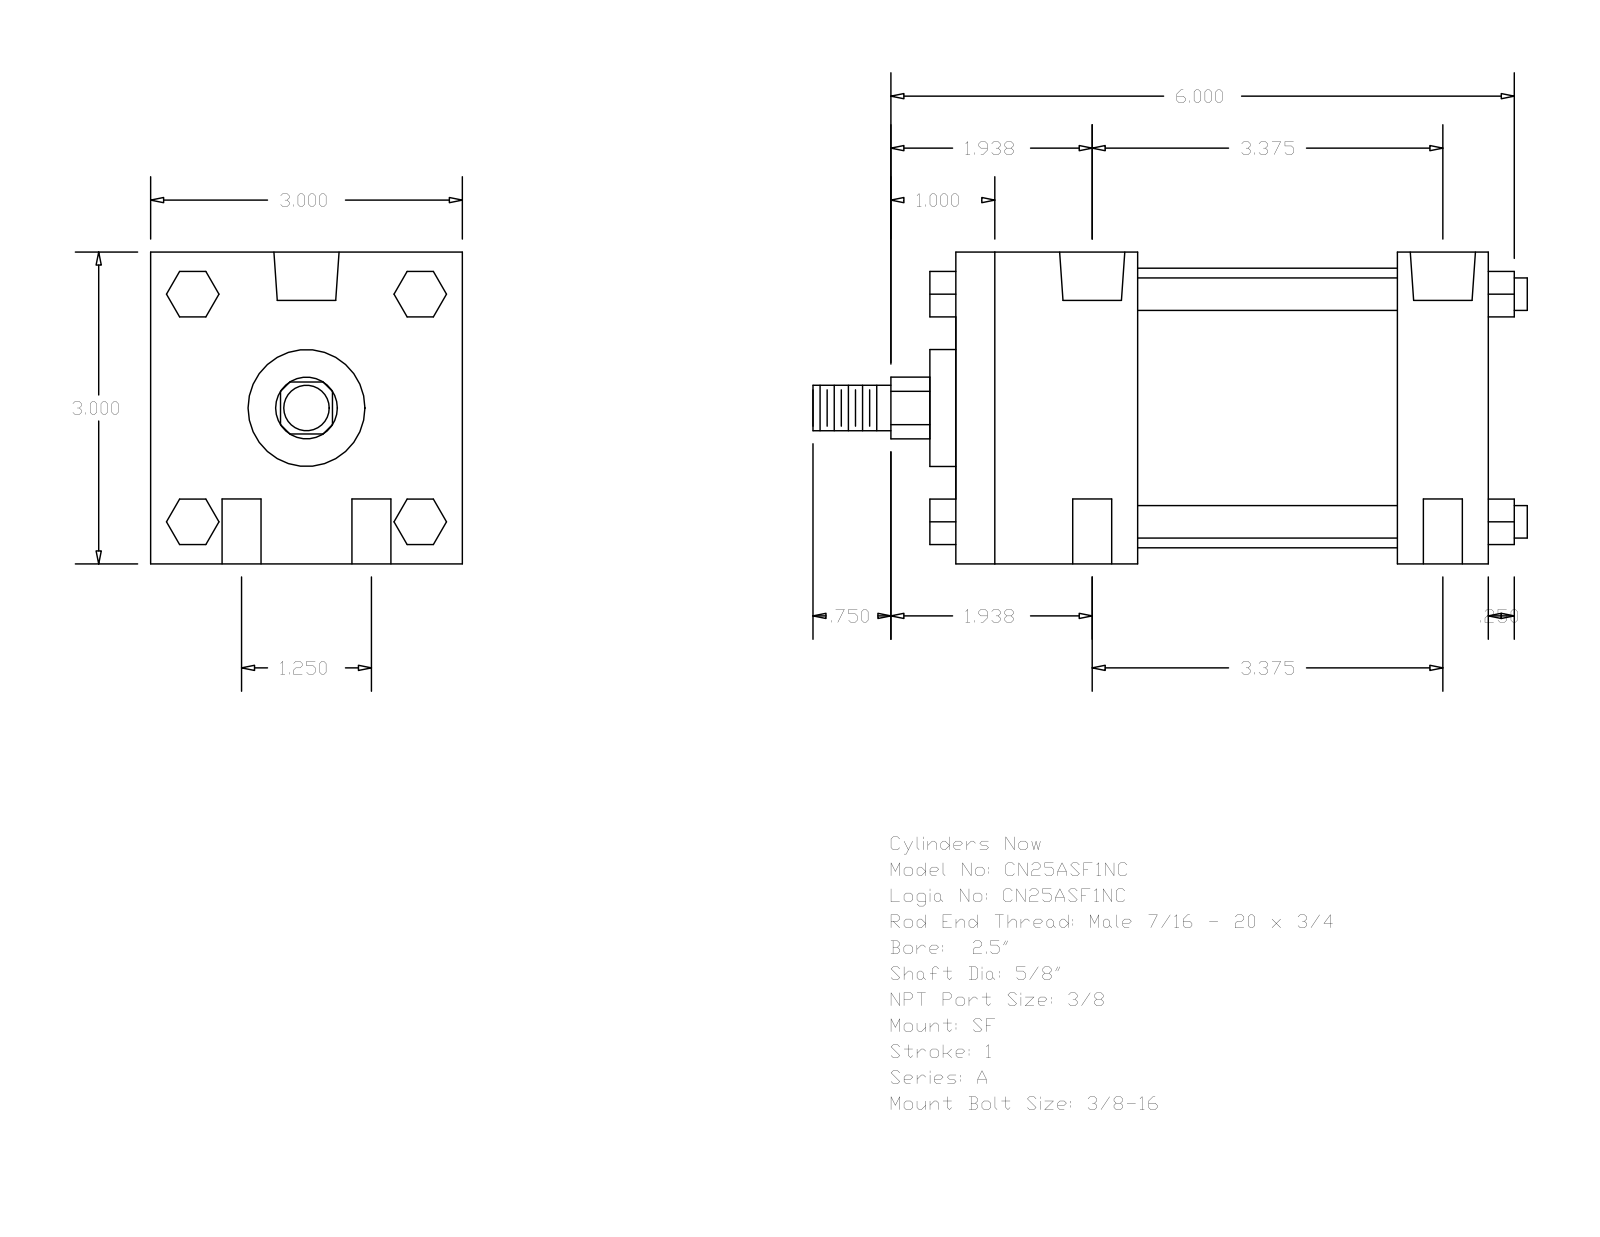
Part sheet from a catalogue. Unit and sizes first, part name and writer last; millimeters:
Units: millimetres
Overall size (bounding box): 174.62 × 76.2 × 76.2
Round holes (diameter × count): ⌀9.53 ×4, ⌀5.56 ×2, ⌀15.93 ×2
Round bosses / shafts (diameter × count): ⌀7.94 ×4, ⌀68.33 ×1, ⌀28.57 ×1, ⌀15.88 ×1, ⌀11.11 ×1
Partial cylindrical surfaces — rounded edges, fillets, slot ends (radius × count): R7.54 ×1
Main face-to-face distances: 76.2, 130.17, 63.5, 44.45, 107.95, 22.22, 85.72, 6.35, 136.52, 50.8
Hole centre spacings: 15.88, 87.19, 85.73, 31.76, 91.42, 90.49
Bodies: 0 solids, 124 faces (94 planar, 30 cylindrical, 0 other)
Part name (STEP PRODUCT): A_SF__0250_0.625
STEP written by: GSSL Pune (CONFIG_CONTROL_DESIGN)
